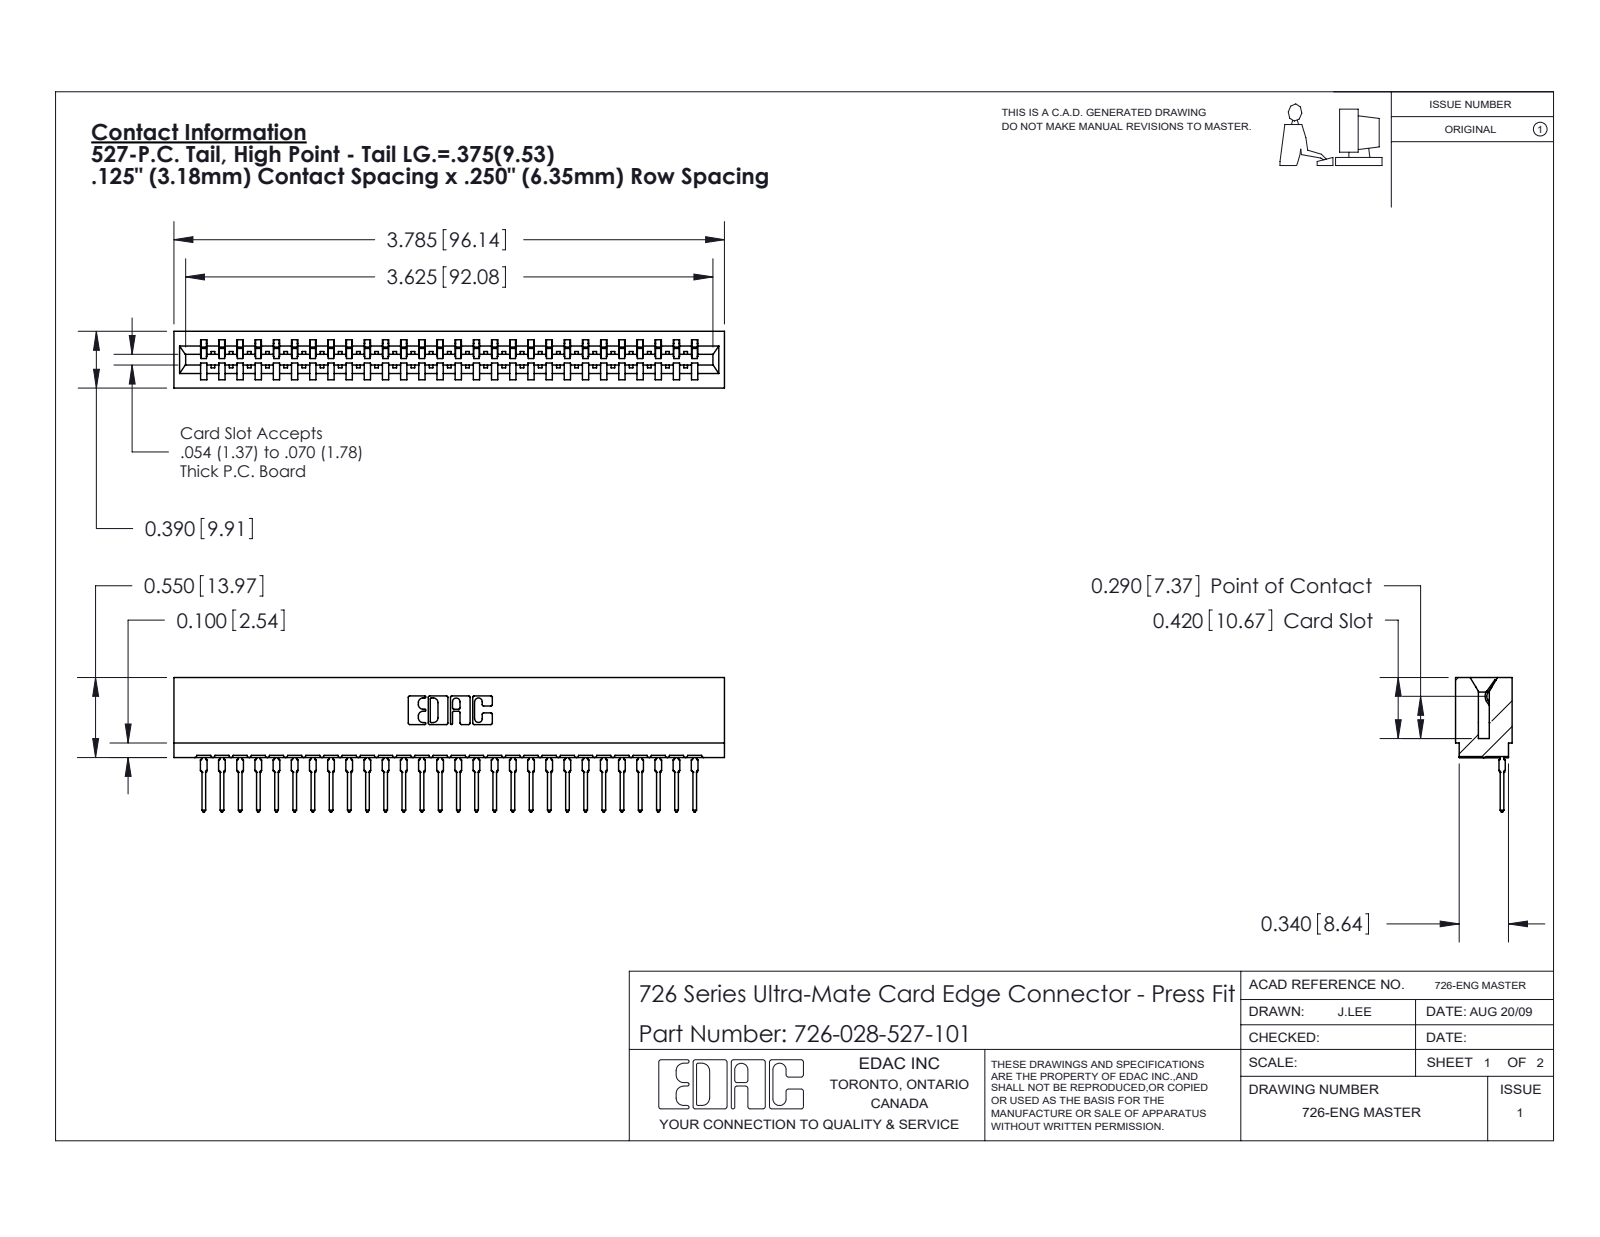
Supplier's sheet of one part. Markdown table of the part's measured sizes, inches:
| quantity | value |
| --- | --- |
| part name | 746-292-001_527; 726-028-527-101; 726 Part_.515 Slot Depth - 01 |
| STEP written by | SolidWorks 2020 (CONFIG_CONTROL_DESIGN) |
| units | inches |
| bodies | 29 solids, 3121 faces (1819 planar, 574 cylindrical, 728 other) |
| overall size | 3.785 × 0.924 × 0.39 |
| volume | 0.53 in³ |
| surface area | 20.49 in² |
| partial cylindrical surfaces (radius × count) | 0.021 × 56, 0.015 × 29, 0.01 × 22, 0.007 × 6, 0.031 × 6, 0.005 × 4, 0.011 × 4, 0.026 × 3 |
| main face-to-face distances | 0.057, 0.333, 0.39, 0.25, 0.025, 0.307, 0.083, 0.275, 0.5, 0.365 |
